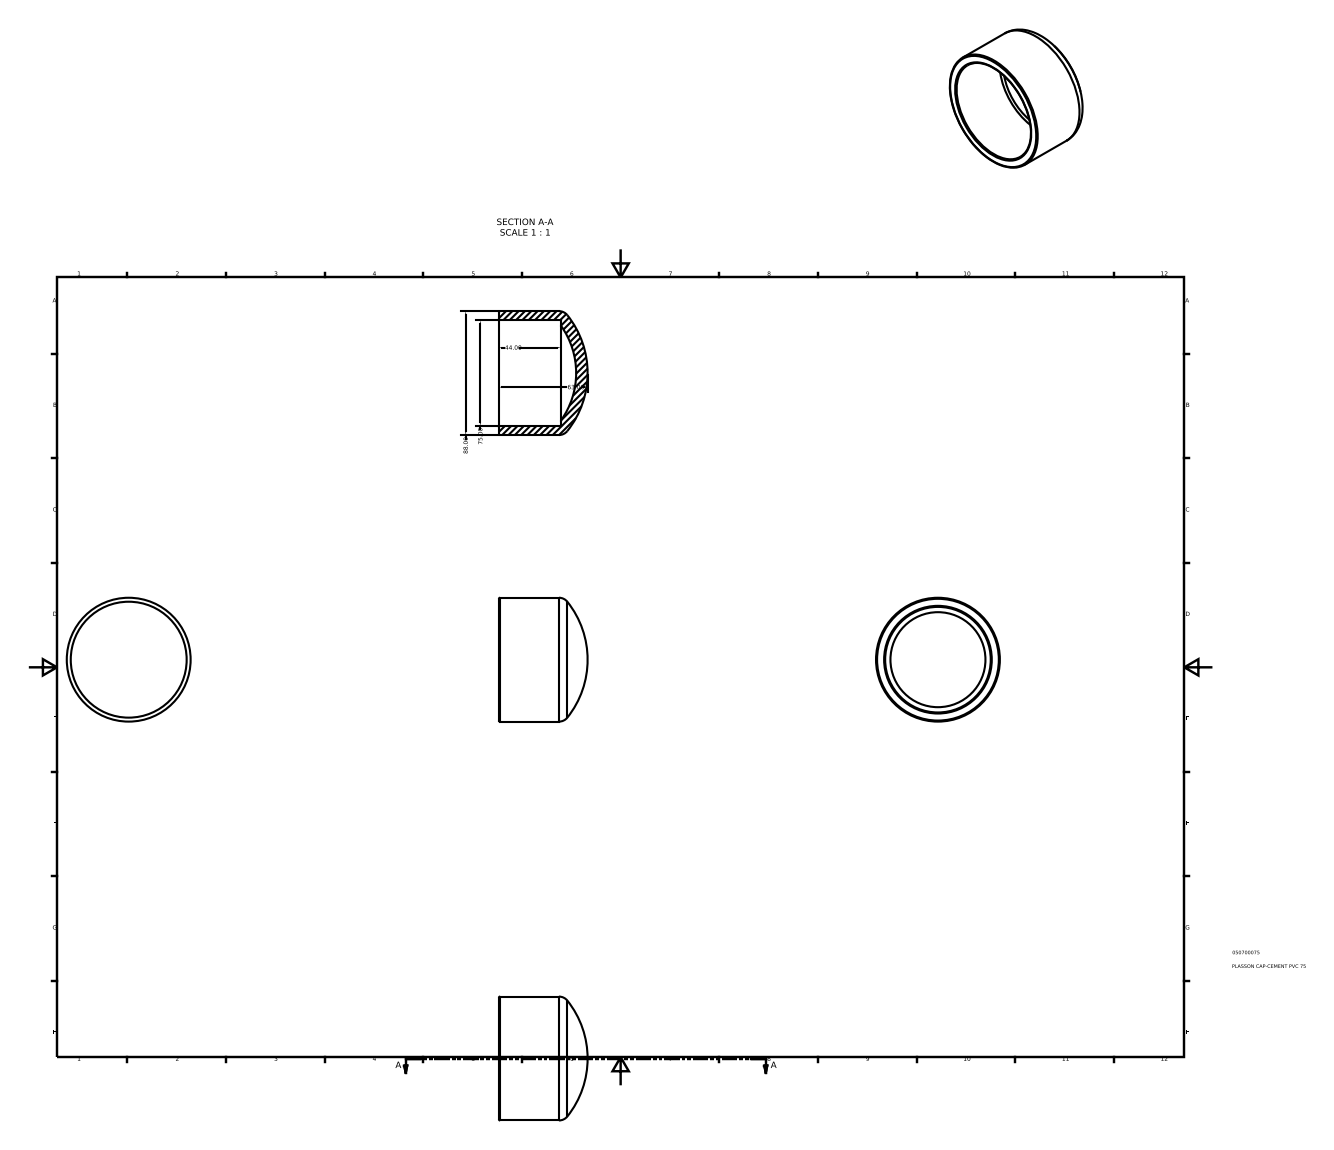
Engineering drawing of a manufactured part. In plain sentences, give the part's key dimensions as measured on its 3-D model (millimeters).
The part is named "050700075". Its 3-D file was written by "Autodesk Inventor 2015 (AUTOMOTIVE_DESIGN)". It is 1 solid with 9 faces: 2 planar, 2 cylindrical and 5 other. Overall it measures 88 by 88 by 63 millimeters. Its volume is 119 548 cubic millimeters and its surface area 36 265 square millimeters. Round holes: 1 of diameter 75. Round bosses or shafts: 1 of diameter 88. The main face-to-face distances are 44.
